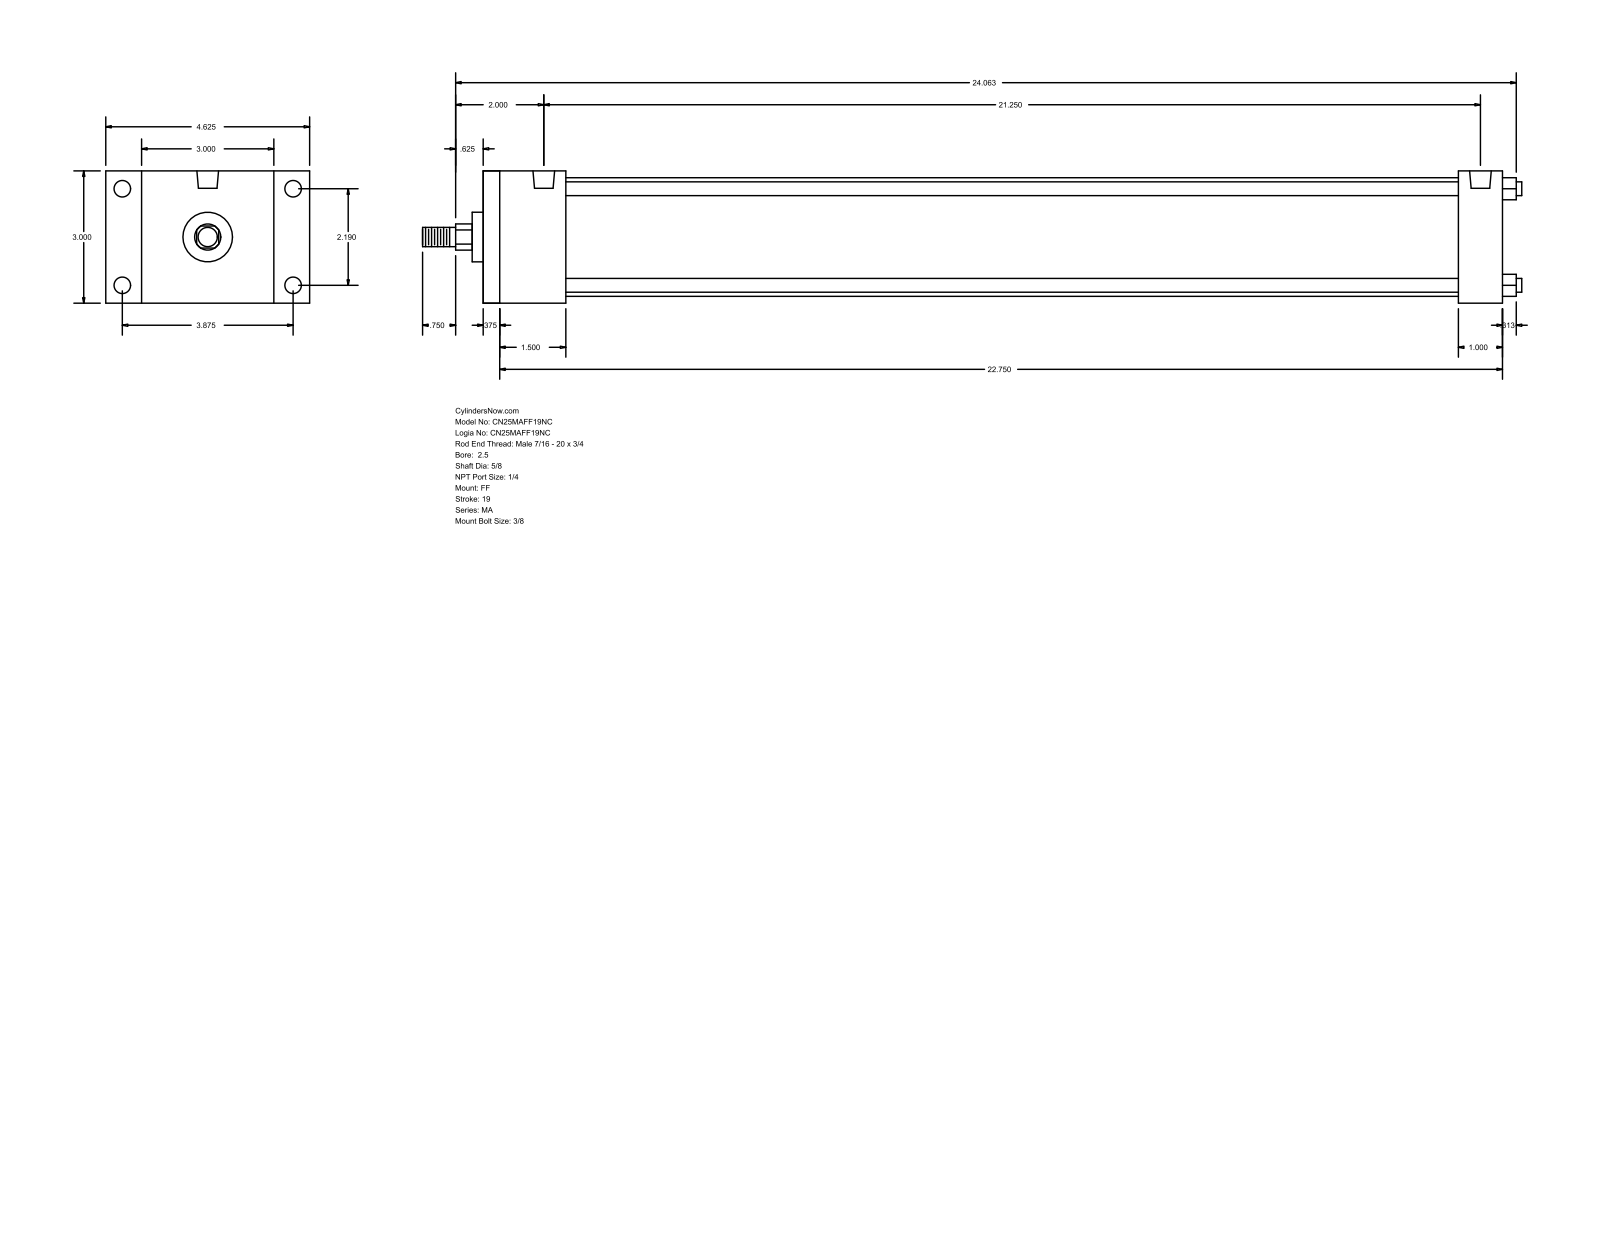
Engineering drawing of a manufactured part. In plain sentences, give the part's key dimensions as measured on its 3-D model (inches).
The part is named "MA_FF__0250_0.625". Its 3-D file was written by "GSSL Pune (CONFIG_CONTROL_DESIGN)". It is 0 solids with 92 faces: 64 planar, 28 cylindrical and 0 other. Overall it measures 24.937 by 4.625 by 3 inches. Round holes: 4 of diameter 0.313, 4 of diameter 0.375, 2 of diameter 0.492. Round bosses or shafts: 4 of diameter 0.313, 1 of diameter 2.69, 1 of diameter 1.125, 1 of diameter 0.625, 1 of diameter 0.437. Partial cylindrical surfaces (rounded edges, fillets, slot ends): 1 of radius 0.297. The main face-to-face distances are 3, 23.125, 22.75, 0.375, 1, 1.875, 22.125, 1.5, 21.75, 20.25. The hole center spacings are 2.19, 3.875, 4.451, 21.25.
